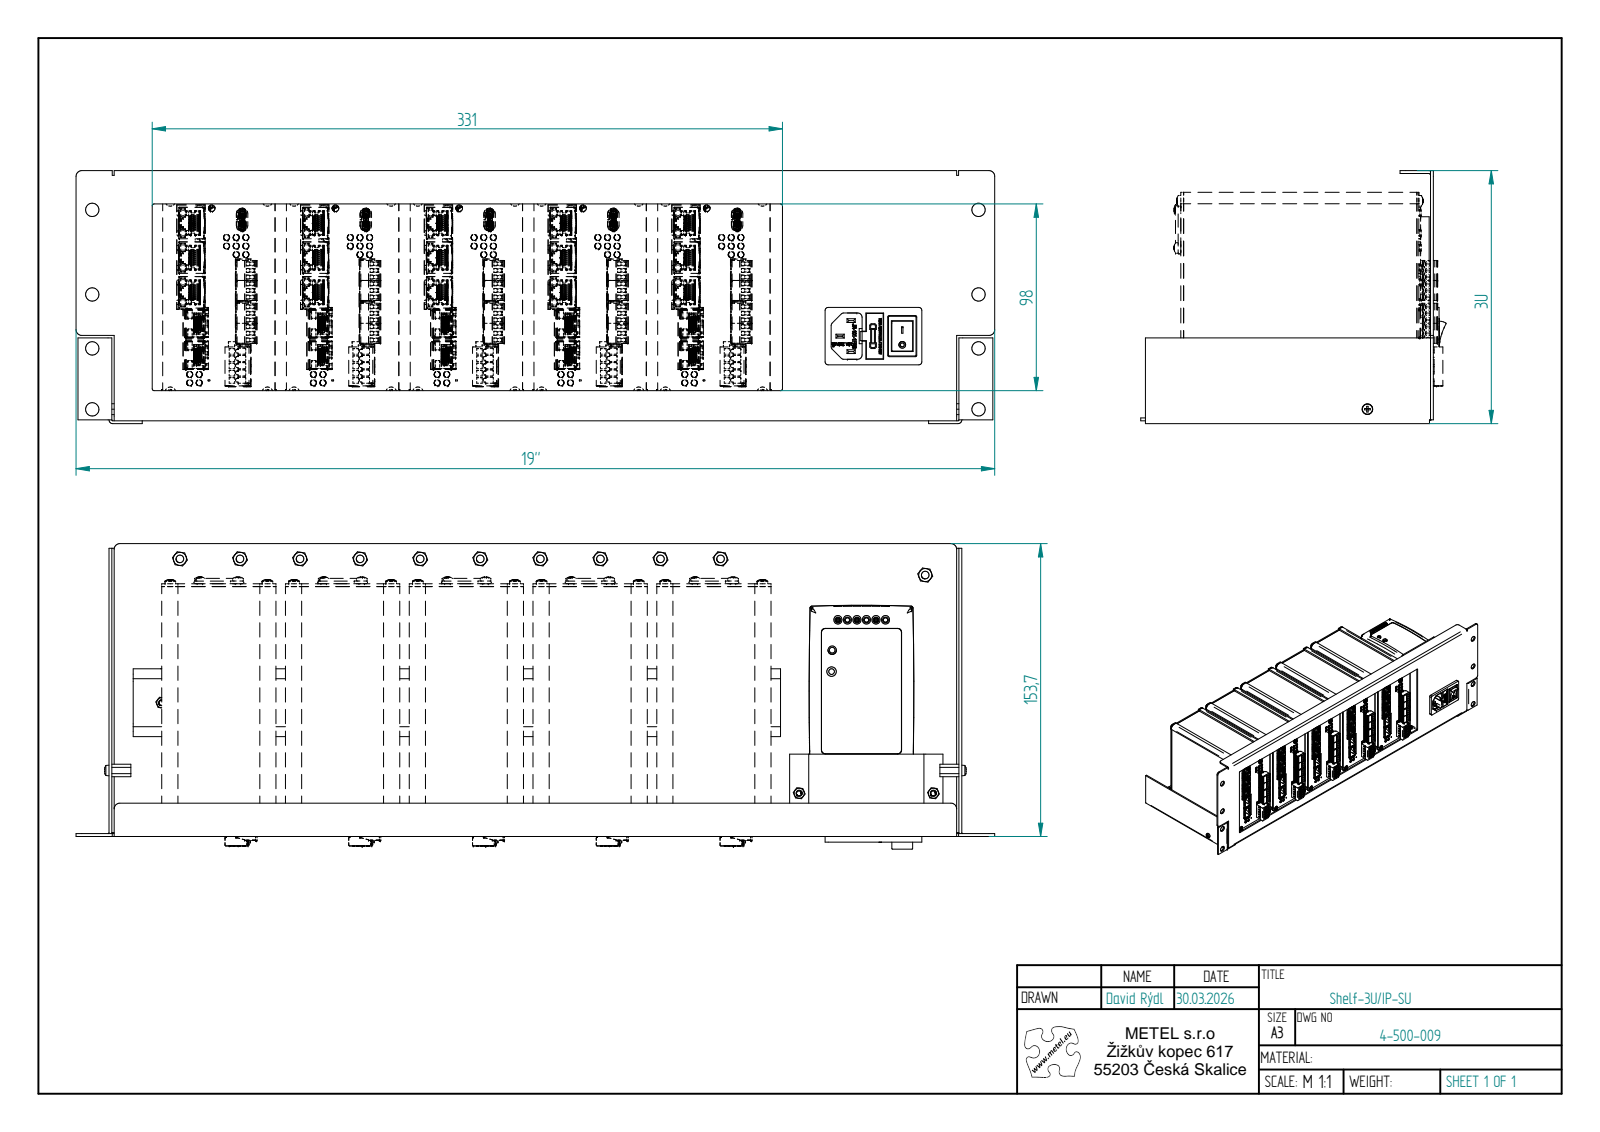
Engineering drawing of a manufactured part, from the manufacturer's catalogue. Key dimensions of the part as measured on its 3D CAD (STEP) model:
Part name (STEP PRODUCT): Shelf-3U_IP-SU; SHELF-ucho-L; SHELF-ui_zrc; distance (+8 more)
STEP written by: Solid Edge (AUTOMOTIVE_DESIGN)
Units: millimetres
Bodies: 695 solids, 81709 faces (42981 planar, 12627 cylindrical, 26101 other)
Overall size (bounding box): 482.5 × 160.36 × 132.8
Volume: 1 045 000 mm³ · Surface area: 1 278 000 mm²
Round holes (diameter × count): ⌀1.5 ×51, ⌀2.1 ×36, ⌀3.25 ×36, ⌀3 ×34, ⌀2.7 ×16, ⌀3.5 ×16, ⌀1.9 ×12, ⌀2.5 ×12, ⌀2.8 ×12, ⌀3.2 ×12, ⌀3.33 ×11, ⌀4.11 ×11
Round bosses / shafts (diameter × count): ⌀1.8 ×42, ⌀3 ×41, ⌀5.6 ×35, ⌀2.9 ×35, ⌀7.5 ×11, ⌀4 ×11, ⌀3.54 ×11, ⌀2 ×9
Partial cylindrical surfaces — rounded edges, fillets, slot ends (radius × count): R0.1 ×420, R0.25 ×408, R0.2 ×243, R0.15 ×175, R0.3 ×165, R0.5 ×165, R0.25 ×158, R0.38 ×148
Main face-to-face distances: 1.5, 65, 57.5, 122.5, 131.15, 130, 7.5, 66.5, 63.5, 124
Hole centre spacings: 3.5, 20, 31.55, 63.1, 94.65, 5, 7, 126.2
